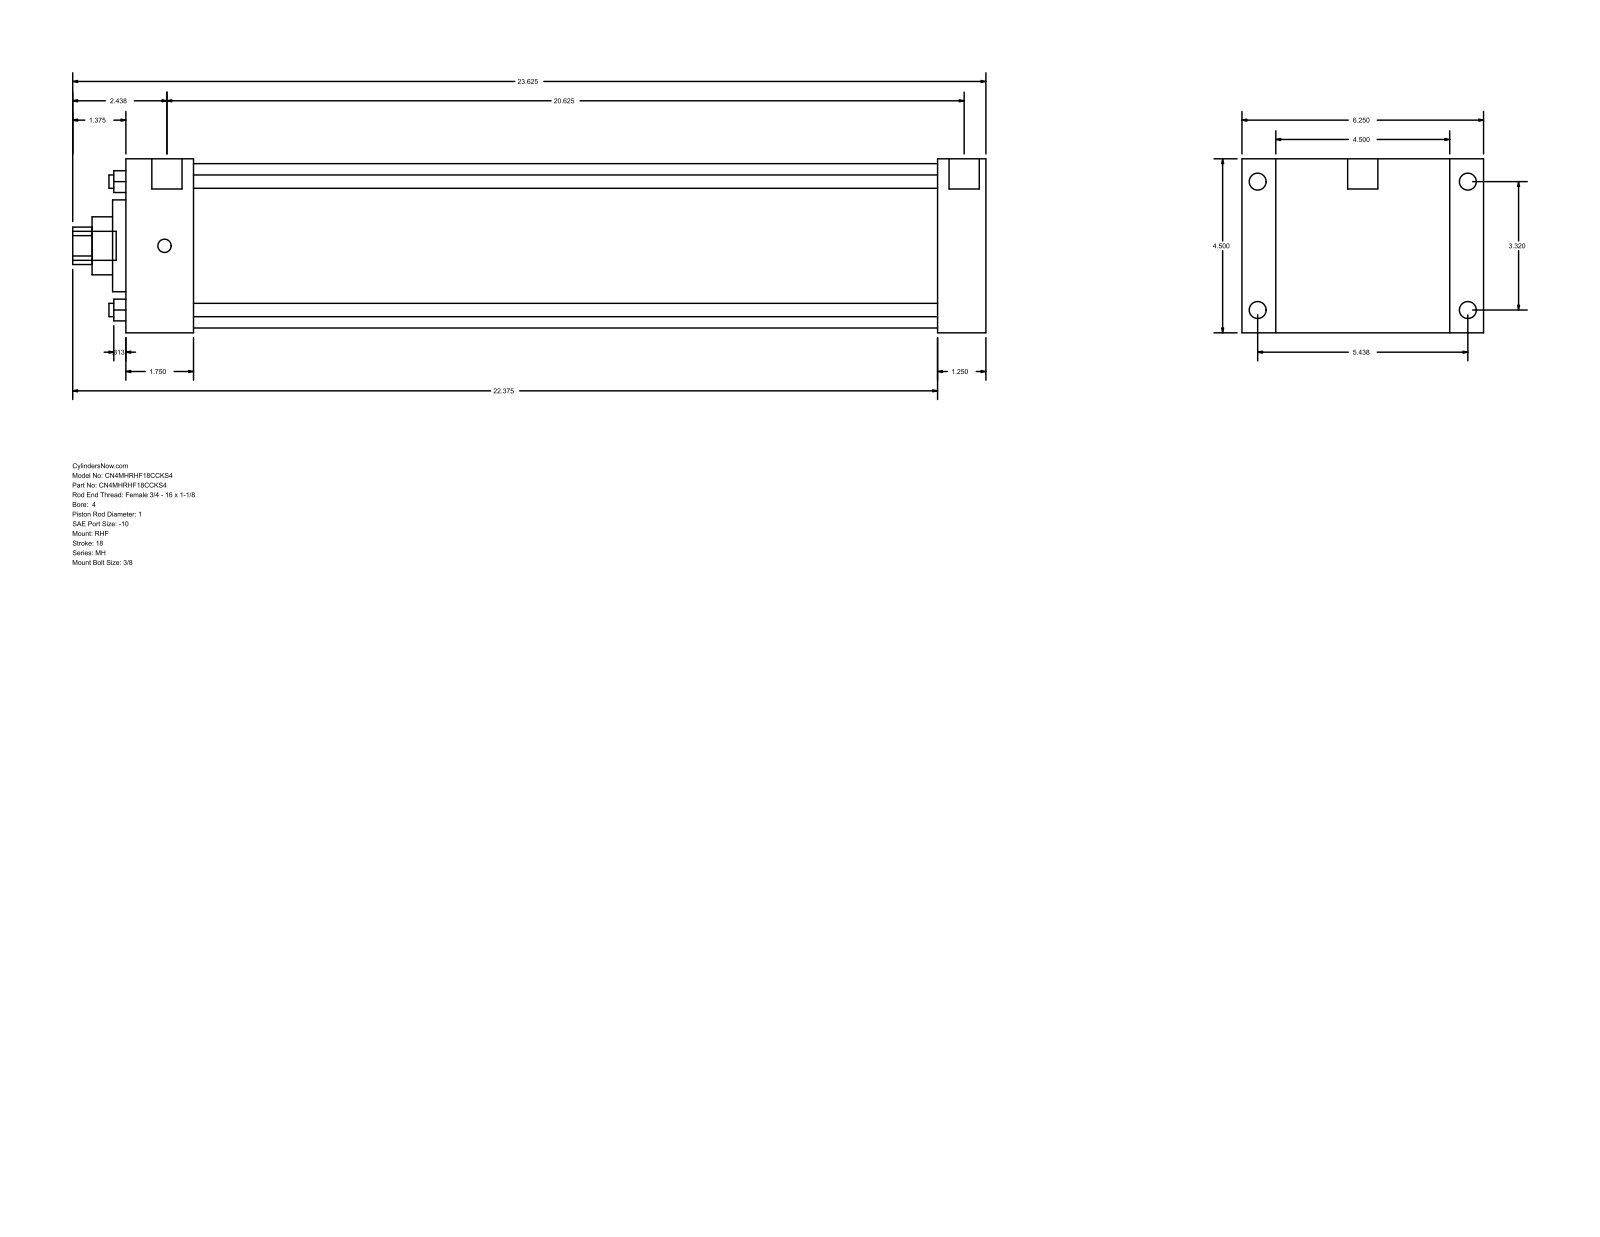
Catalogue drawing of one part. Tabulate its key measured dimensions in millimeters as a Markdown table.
| quantity | value |
| --- | --- |
| part name | MH_RHF__0400_1 |
| STEP written by | GSSL Pune (CONFIG_CONTROL_DESIGN) |
| units | millimeters |
| bodies | 0 solids, 90 faces (61 planar, 29 cylindrical, 0 other) |
| overall size | 600.08 × 158.75 × 114.3 |
| round holes (diameter × count) | 8.76 × 4, 25.4 × 1, 38.1 × 1, 60.33 × 1, 107.95 × 1 |
| round bosses / shafts (diameter × count) | 11.13 × 4, 8.73 × 4, 19.84 × 2, 19.05 × 1 |
| partial cylindrical surfaces (radius × count) | 12.29 × 1 |
| main face-to-face distances | 114.3, 565.16, 533.41, 31.75, 22.23, 136.53, 44.46, 488.95, 520.7, 158.76 |
| hole center spacings | 59.62, 84.32, 119.25 |
